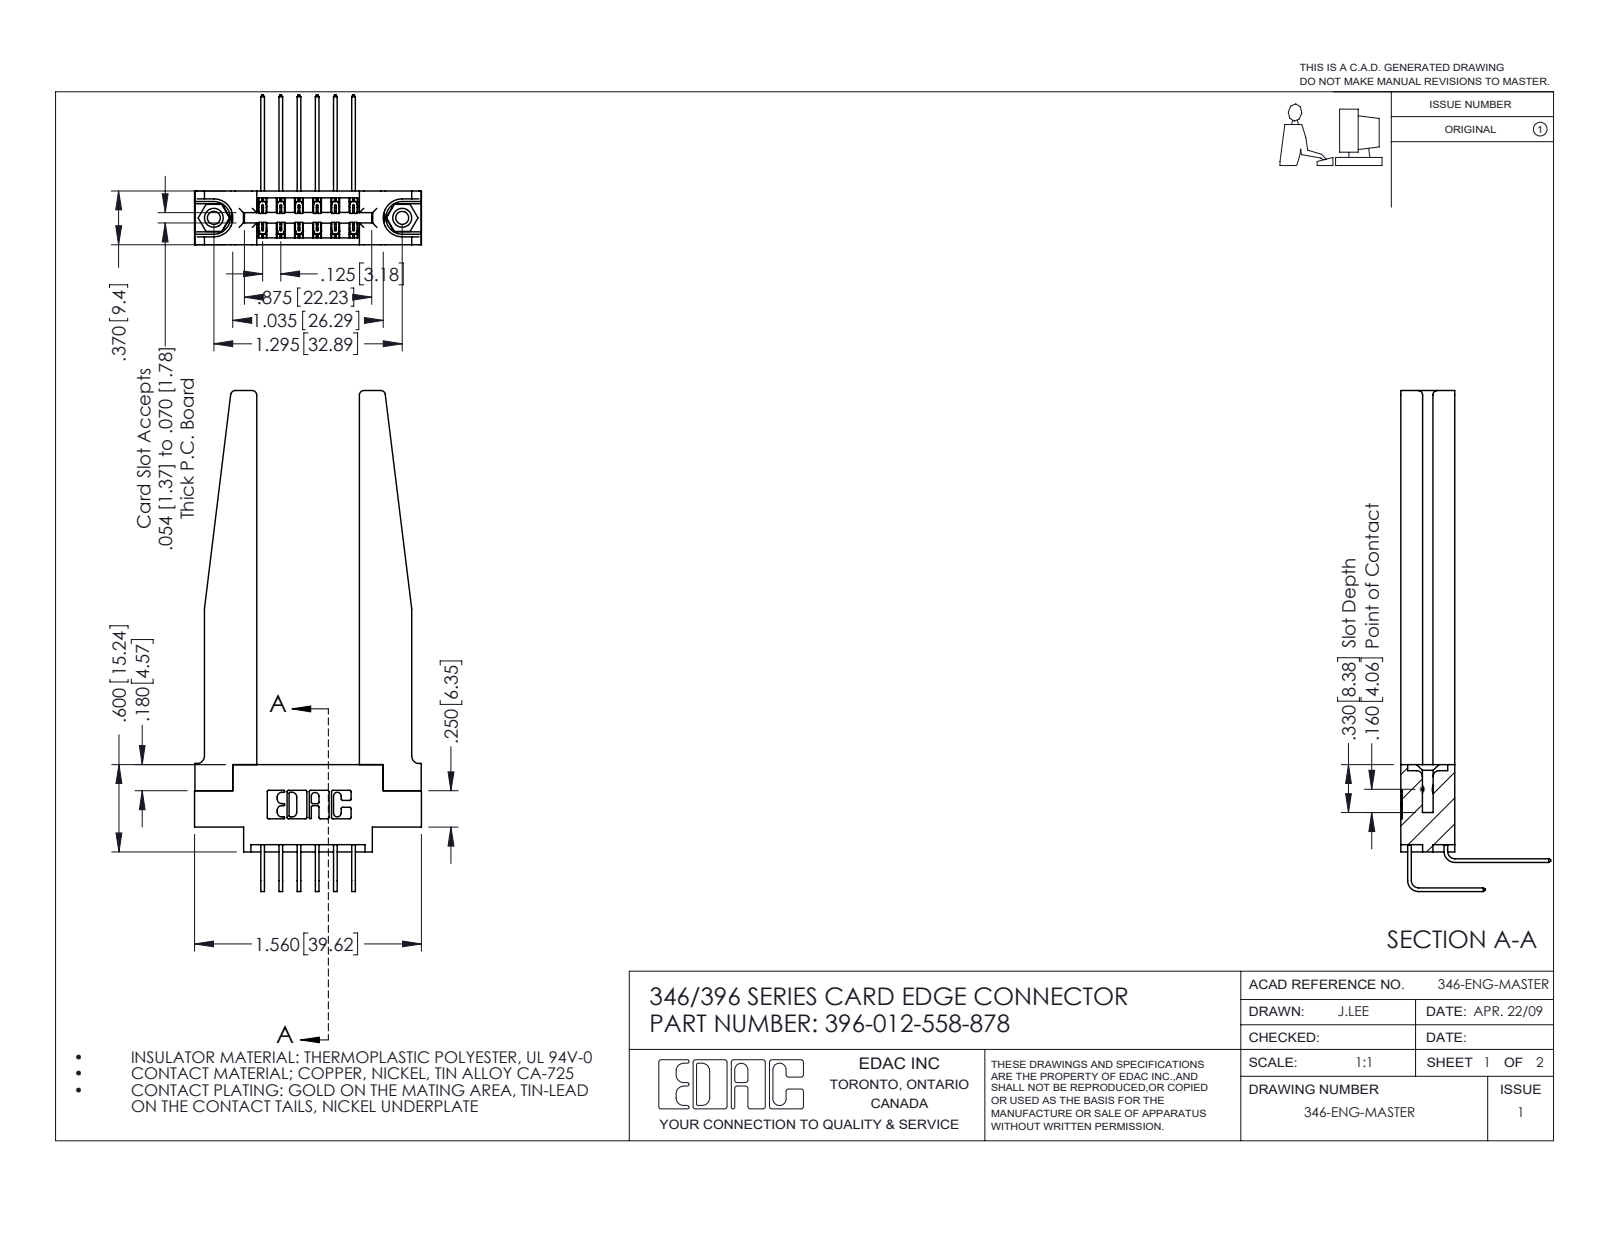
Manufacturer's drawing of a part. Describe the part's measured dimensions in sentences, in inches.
The part is named "345-292-001_558 559 Tail - 1; 396-012-558-878; 345-292-001_558 Tail - 2; 346 Part_0.170 Offset - 0.156 Dia-TH (+2 more)". Its 3-D file was written by "SolidWorks 2016 (CONFIG_CONTROL_DESIGN)". It is 17 solids with 1008 faces: 666 planar, 290 cylindrical and 52 other. Overall it measures 3.443 by 1.56 by 1.03 inches. Its volume is 0.635 cubic inches and its surface area 17.5 square inches. Round holes: 2 of diameter 0.089, 2 of diameter 0.125, 2 of diameter 0.156, 1 of diameter 0.064. Round bosses or shafts: 2 of diameter 0.155. Partial cylindrical surfaces (rounded edges, fillets, slot ends): 22 of radius 0.01, 18 of radius 0.006, 8 of radius 0.03, 6 of radius 0.007, 6 of radius 0.031, 4 of radius 0.05, 3 of radius 0.026, 2 of radius 0.014. The main face-to-face distances are 0.37, 0.15, 0.22, 0.25, 0.072, 0.706, 0.048, 0.148, 0.322, 0.102. The hole center spacings are 0.246, 1.092, 1.295.
